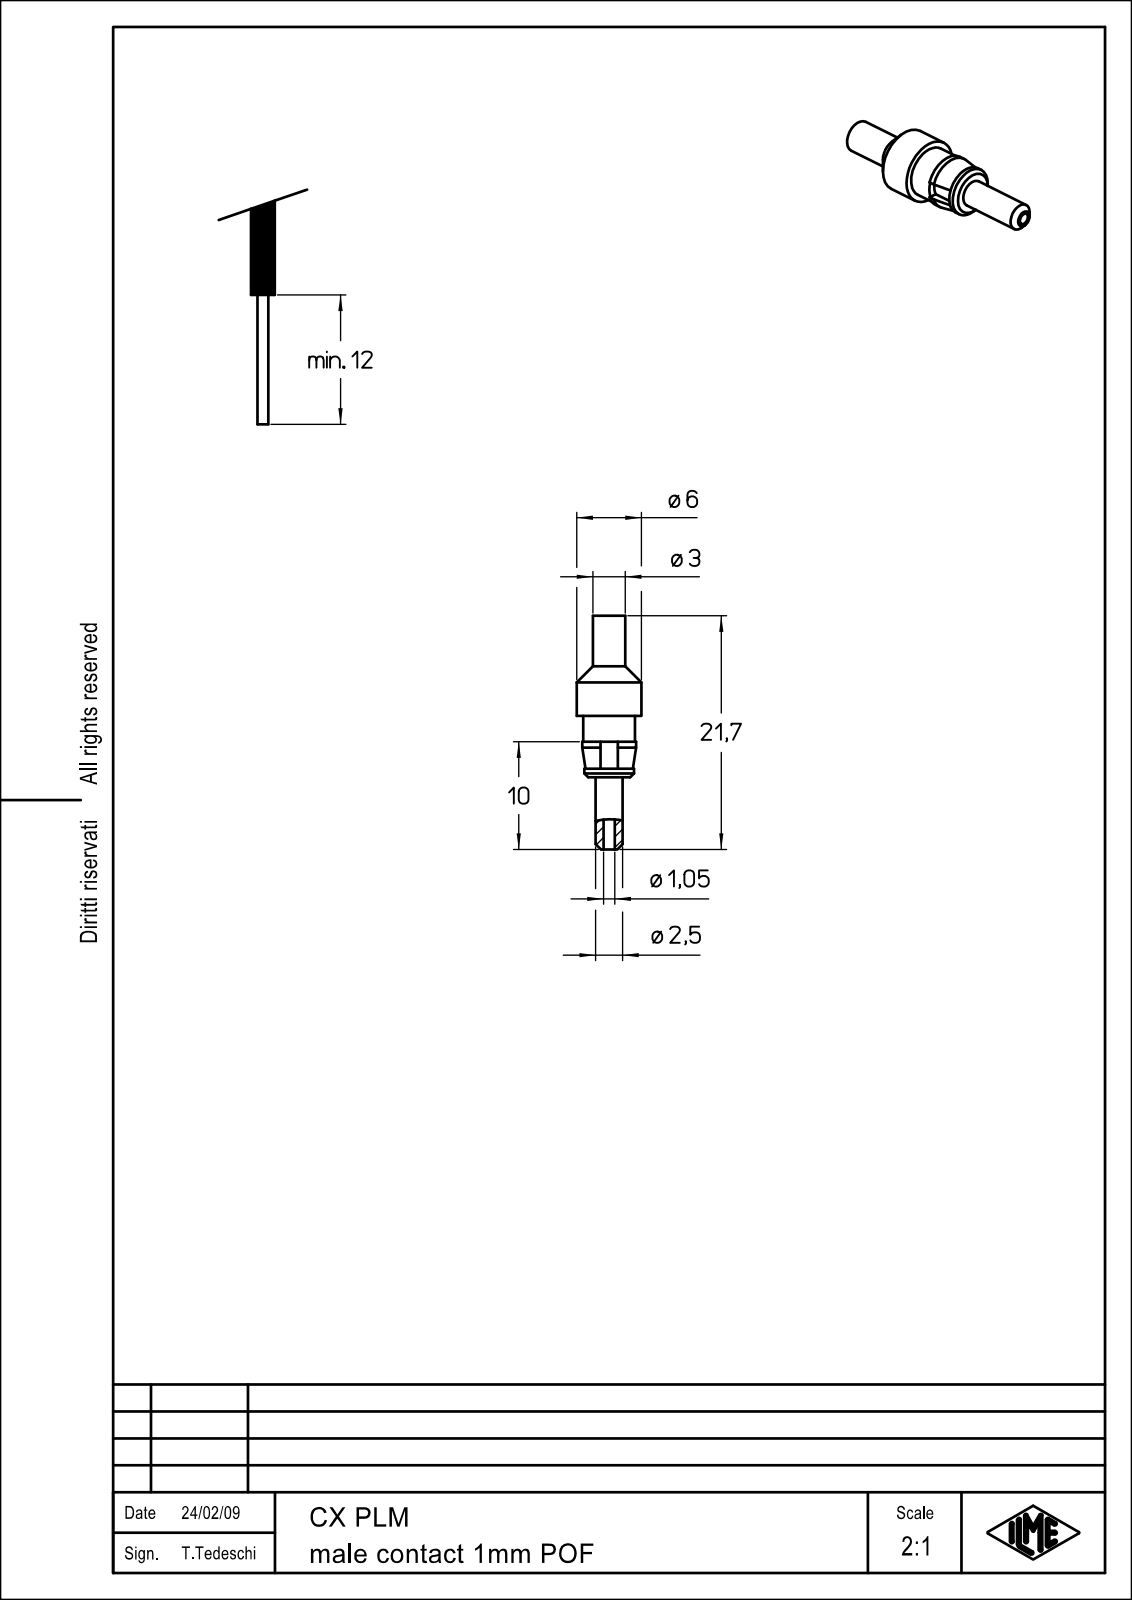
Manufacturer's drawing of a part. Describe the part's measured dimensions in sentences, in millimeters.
The part is named "CX_PLM". Its 3-D file was written by "CoCreate Modeling 16.00A 16-Aug-2008 (C) Parametric Technology GmbH (AUTOMOTIVE_DESIGN)". It is 1 solid with 37 faces: 10 planar, 18 cylindrical and 9 other. Overall it measures 21.7 by 6 by 6 millimeters. Its volume is 230 cubic millimeters and its surface area 411 square millimeters. Round holes: 1 of diameter 1.05, 1 of diameter 2.2. Round bosses or shafts: 1 of diameter 6, 1 of diameter 5, 1 of diameter 4.8, 1 of diameter 4.6, 1 of diameter 3, 1 of diameter 2.5. Partial cylindrical surfaces (rounded edges, fillets, slot ends): 1 of radius 1.75. The main face-to-face distances are 5.7, 9.3, 15, 11.7, 2.4, 3.3, 14.2, 4.9, 2.5, 0.8.
